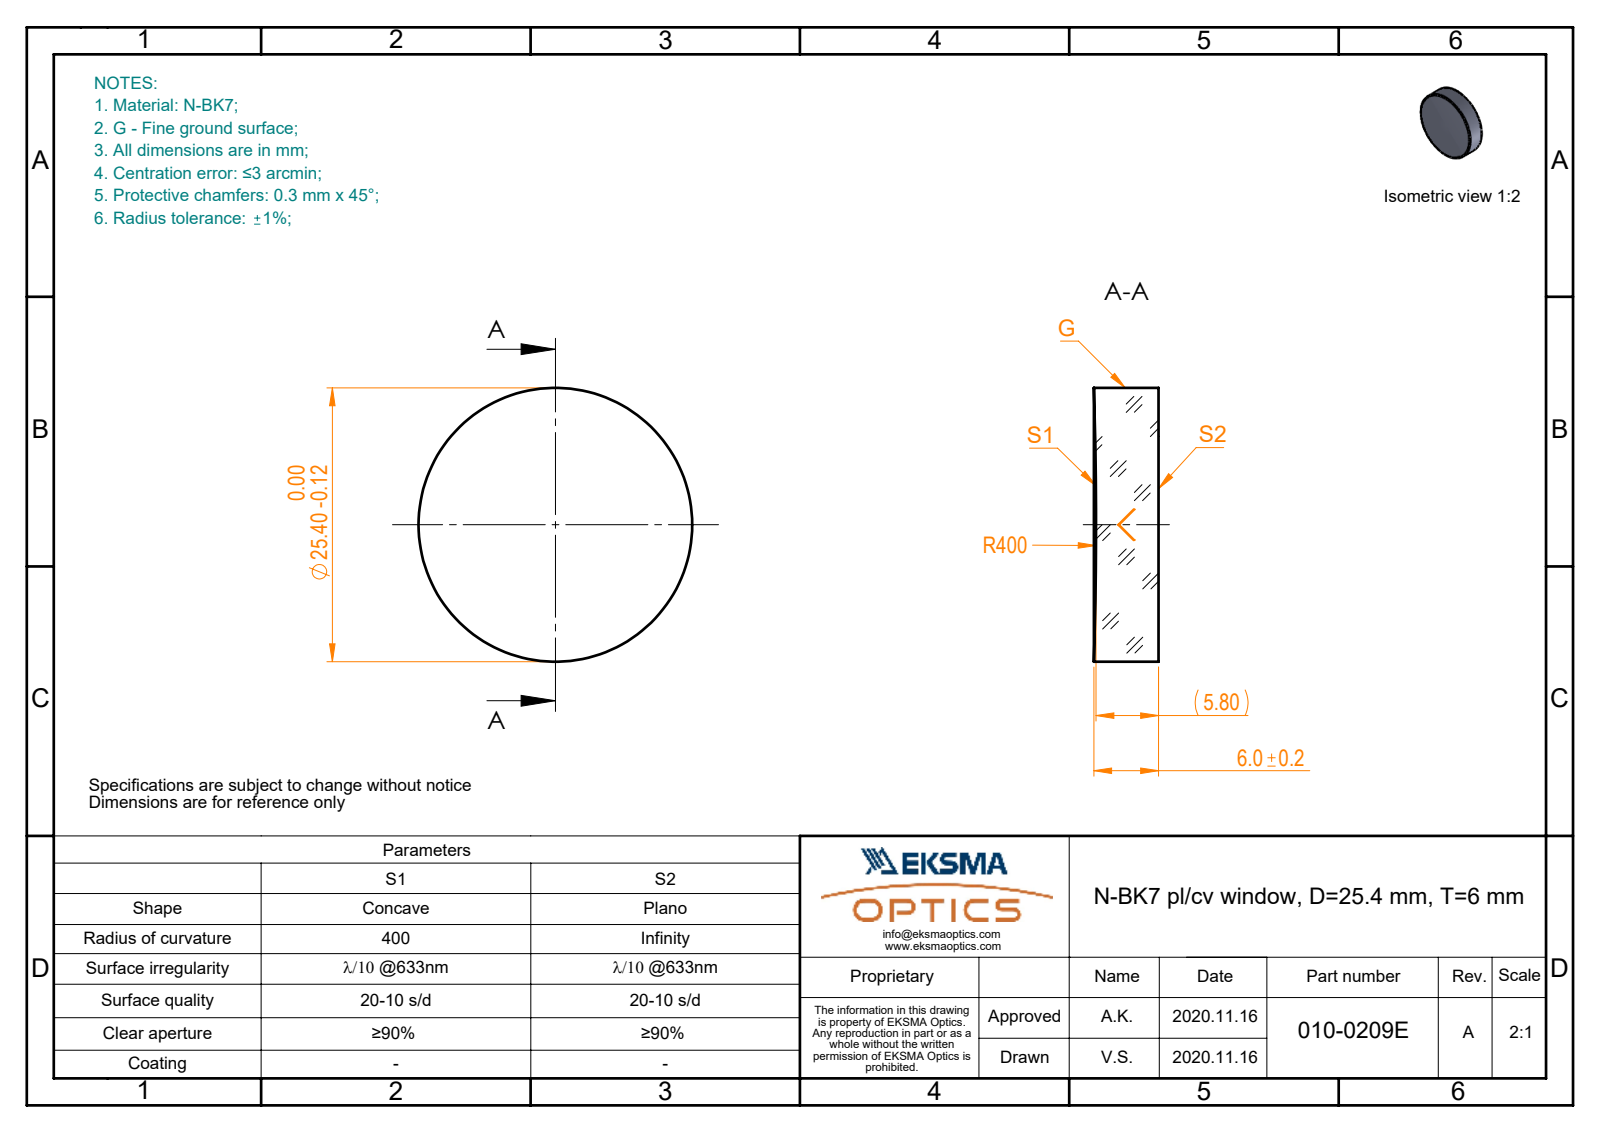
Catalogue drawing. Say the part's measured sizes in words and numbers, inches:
The part is named "010-0209E_N-BK7_PCV_window". Its 3-D file was written by "SolidWorks 2019 (CONFIG_CONTROL_DESIGN)". It is 1 solid with 5 faces: 1 planar, 2 cylindrical and 2 other. Overall it measures 1 by 1 by 0.236 inches. Its volume is 0.182 cubic inches and its surface area 2.313 square inches. Round bosses or shafts: 1 of diameter 1.
